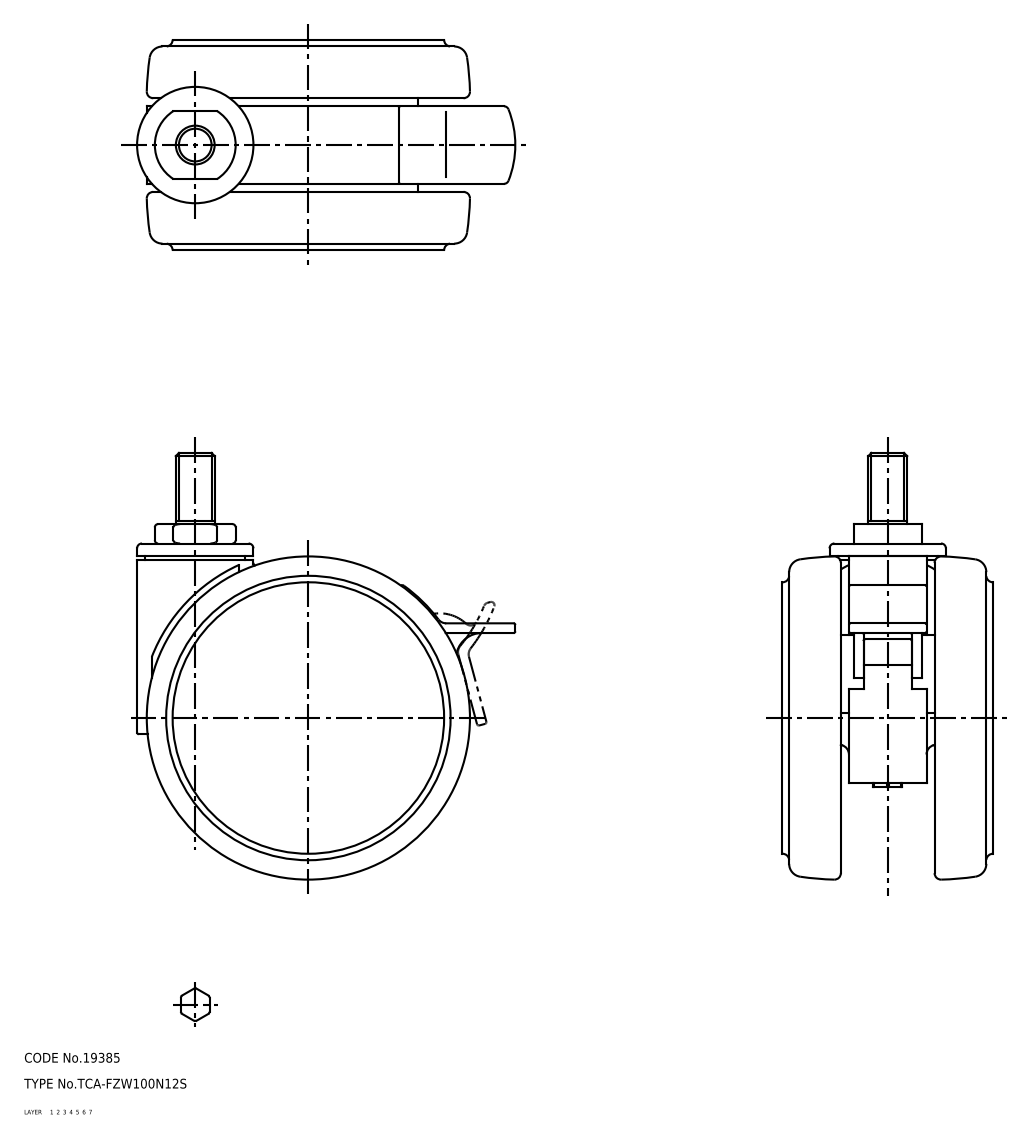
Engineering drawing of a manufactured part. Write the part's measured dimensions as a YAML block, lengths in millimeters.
part_name: "caster; TCA-FZW100N12S"
step_written_by: "SolidWorks 2015 (AUTOMOTIVE_DESIGN)"
units: millimeters
bodies: {solids: 1, faces: 2495, planar: 865, cylindrical: 1191, other: 439}
overall_size: [132, 117.03, 65.2]
volume: 303958
surface_area: 124924
round_holes:
  - {diameter: 2.8, count: 1}
  - {diameter: 3, count: 1}
  - {diameter: 3.3, count: 1}
  - {diameter: 4.1, count: 1}
  - {diameter: 4.2, count: 1}
  - {diameter: 6, count: 1}
  - {diameter: 9.1, count: 1}
  - {diameter: 10, count: 1}
  - {diameter: 10.1, count: 1}
  - {diameter: 10.5, count: 1}
  - {diameter: 11, count: 1}
  - {diameter: 12, count: 1}
round_bosses_or_shafts:
  - {diameter: 87.8, count: 1}
  - {diameter: 36, count: 1}
  - {diameter: 31, count: 1}
  - {diameter: 27.9, count: 1}
  - {diameter: 27.6, count: 1}
  - {diameter: 20, count: 1}
  - {diameter: 19, count: 1}
  - {diameter: 18, count: 1}
partial_cylinders:
  - {radius: 0.5, count: 236}
  - {radius: 1.2, count: 160}
  - {radius: 1, count: 87}
  - {radius: 2, count: 25}
  - {radius: 1.5, count: 23}
  - {radius: 0.2, count: 18}
  - {radius: 0.3, count: 12}
  - {radius: 3, count: 8}
face_to_face_distances: [1.8, 61.6, 63.4, 3.6, 59.8, 14.5, 16.3, 45.3, 18.1, 47.1]
hole_center_spacings: [22.78, 29.45, 44]
